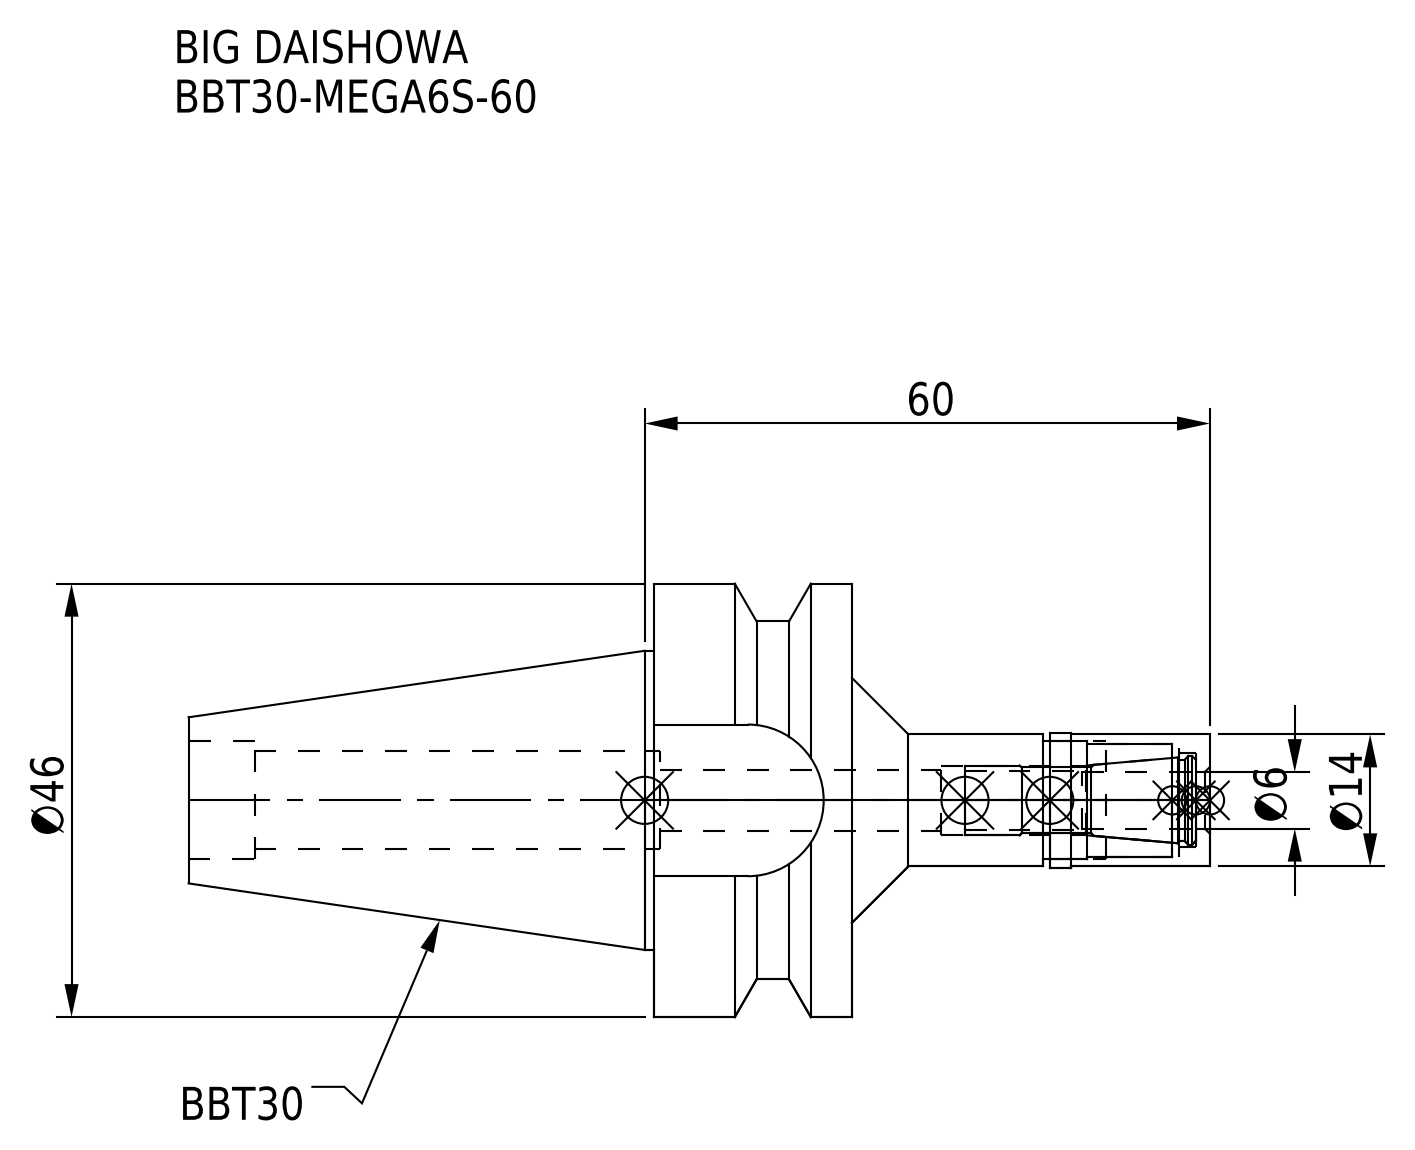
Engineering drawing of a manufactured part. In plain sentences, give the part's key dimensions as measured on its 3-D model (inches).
The part is named "BBT30-MEGA6S-60; MGN6S_1.stp; BBT30-MEGA6S-60-060.stp; BBT30MS06060-060_ASM.stp (+3 more)". Its 3-D file was written by "SolidWorks 2019 (CONFIG_CONTROL_DESIGN)". It is 2 solids with 71 faces: 21 planar, 38 cylindrical and 12 other. Overall it measures 4.268 by 1.811 by 1.811 inches. Its volume is 3.283 cubic inches and its surface area 24.72 square inches. Round holes: 1 of diameter 0.24, 1 of diameter 0.252, 1 of diameter 0.291, 1 of diameter 0.394, 1 of diameter 0.409, 1 of diameter 0.472, 1 of diameter 0.492. Round bosses or shafts: 1 of diameter 1.811, 1 of diameter 1.25, 1 of diameter 0.563, 1 of diameter 0.551, 1 of diameter 0.551, 1 of diameter 0.492, 1 of diameter 0.472. Partial cylindrical surfaces (rounded edges, fillets, slot ends): 1 of radius 0.317, 1 of radius 0.748. The main face-to-face distances are 0.827, 1.283, 2.772, 1.945, 1.496, 2.323, 4.268, 0.634, 0.028, 0.539.
